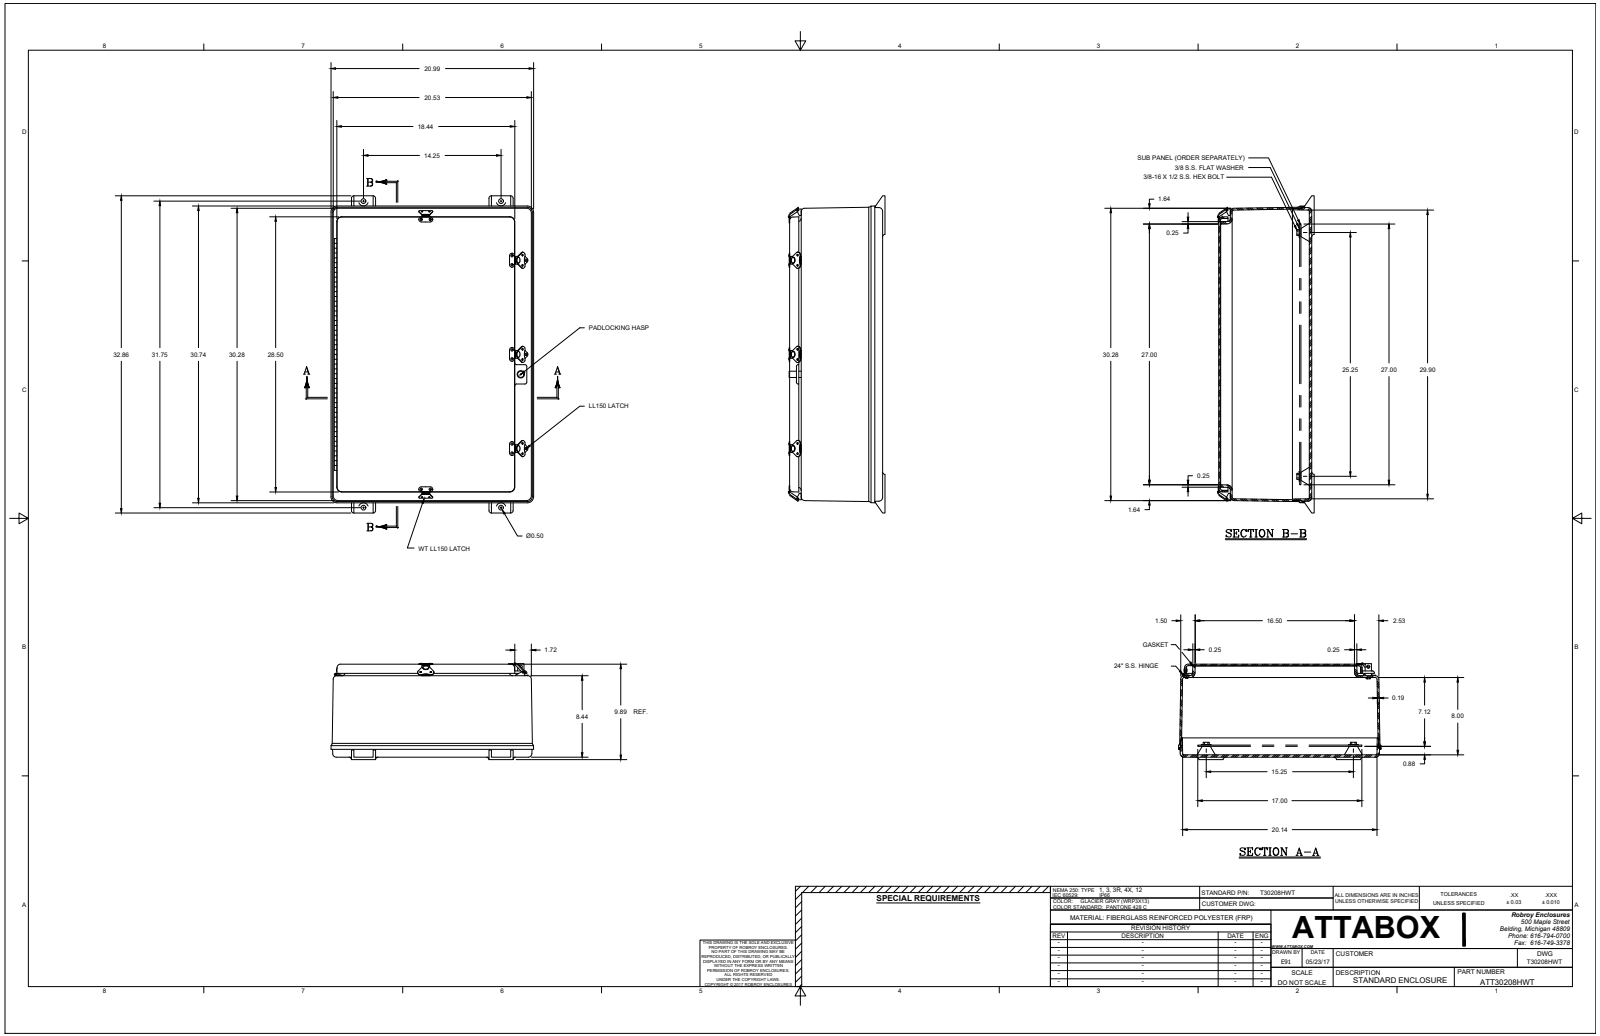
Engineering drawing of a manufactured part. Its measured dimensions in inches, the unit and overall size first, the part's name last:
Units: inches
Overall size (bounding box): 32.844 × 21 × 10.24
Round holes (diameter × count): ⌀0.13 ×36, ⌀0.063 ×20, ⌀0.138 ×10, ⌀0.187 ×10, ⌀0.065 ×5, ⌀0.563 ×4, ⌀0.065 ×3, ⌀0.135 ×3, ⌀0.156 ×3, ⌀0.51 ×2, ⌀0.51 ×2, ⌀0.125 ×1
Round bosses / shafts (diameter × count): ⌀0.14 ×20, ⌀0.297 ×8, ⌀0.5 ×5, ⌀0.2 ×3, ⌀0.135 ×3, ⌀0.25 ×1, ⌀0.201 ×1
Partial cylindrical surfaces — rounded edges, fillets, slot ends (radius × count): R0.01 ×127, R0.25 ×24, R0.03 ×20, R0.375 ×17, R0.313 ×16, R0.187 ×13, R0.5 ×12, R0.125 ×10
Main face-to-face distances: 0.187, 0.25, 0.156, 9.625, 9.375, 9.219, 9.469, 8.437, 8.25, 8
Hole centre spacings: 9.75, 7.5, 15.5, 0.858, 1.542, 19.5, 1, 8
Volume: 481.9 in³ · Surface area: 5 118 in²
Bodies: 63 solids, 1747 faces (659 planar, 702 cylindrical, 386 other)
Part name (STEP PRODUCT): T30208HWT
STEP written by: SolidWorks 2018 (AUTOMOTIVE_DESIGN)
